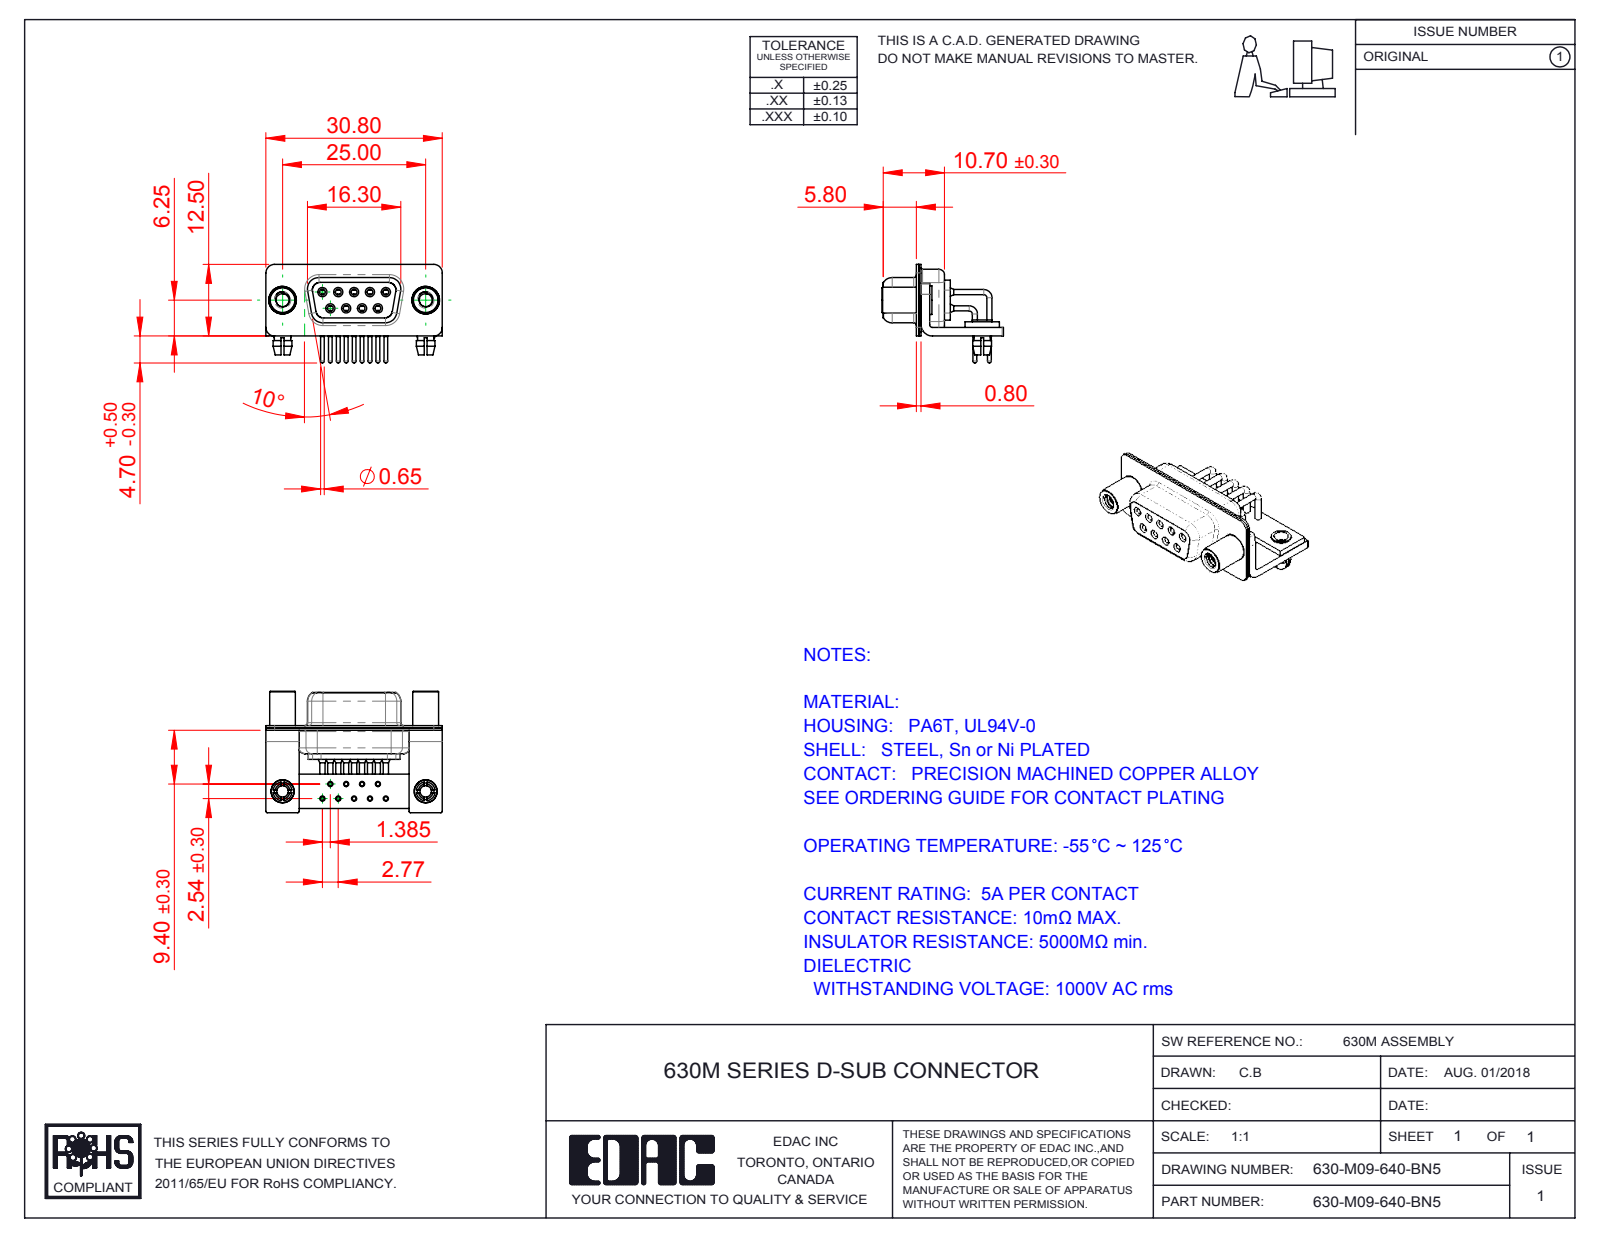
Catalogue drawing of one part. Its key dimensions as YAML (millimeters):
part_name: "630M Stabilizer Bracket; 630-M09-640-BN5; 630M Contact Row 2; 630M Contact Row 1 (+6 more)"
step_written_by: "SolidWorks 2016 (CONFIG_CONTROL_DESIGN)"
units: millimeters
bodies: {solids: 19, faces: 966, planar: 278, cylindrical: 458, other: 230}
overall_size: [30.8, 21.2, 17.2]
volume: 2364
surface_area: 6238
round_holes:
  - {diameter: 2, count: 11}
  - {diameter: 0.9, count: 9}
  - {diameter: 1, count: 9}
  - {diameter: 1.1, count: 9}
  - {diameter: 1.7, count: 9}
  - {diameter: 1.8, count: 9}
  - {diameter: 2.26, count: 2}
  - {diameter: 2.5, count: 2}
  - {diameter: 3.2, count: 2}
  - {diameter: 4, count: 2}
  - {diameter: 4.8, count: 2}
round_bosses_or_shafts:
  - {diameter: 1.6, count: 9}
  - {diameter: 1.5, count: 9}
  - {diameter: 0.9, count: 9}
  - {diameter: 0.65, count: 9}
  - {diameter: 5, count: 2}
  - {diameter: 4.9, count: 2}
  - {diameter: 4.5, count: 2}
  - {diameter: 4, count: 2}
partial_cylinders:
  - {radius: 0.25, count: 16}
  - {radius: 1.5, count: 16}
  - {radius: 2, count: 13}
  - {radius: 1.35, count: 8}
  - {radius: 1.6, count: 8}
  - {radius: 0.5, count: 5}
  - {radius: 0.6, count: 4}
  - {radius: 0.65, count: 4}
face_to_face_distances: [0.4, 1.5, 0.8, 2.3, 1.9, 1, 9.35, 1.45, 8.5, 8.95]
hole_center_spacings: [2.77, 5.54, 3.16, 4.87, 8.31, 2.89, 2.9, 5.03]
